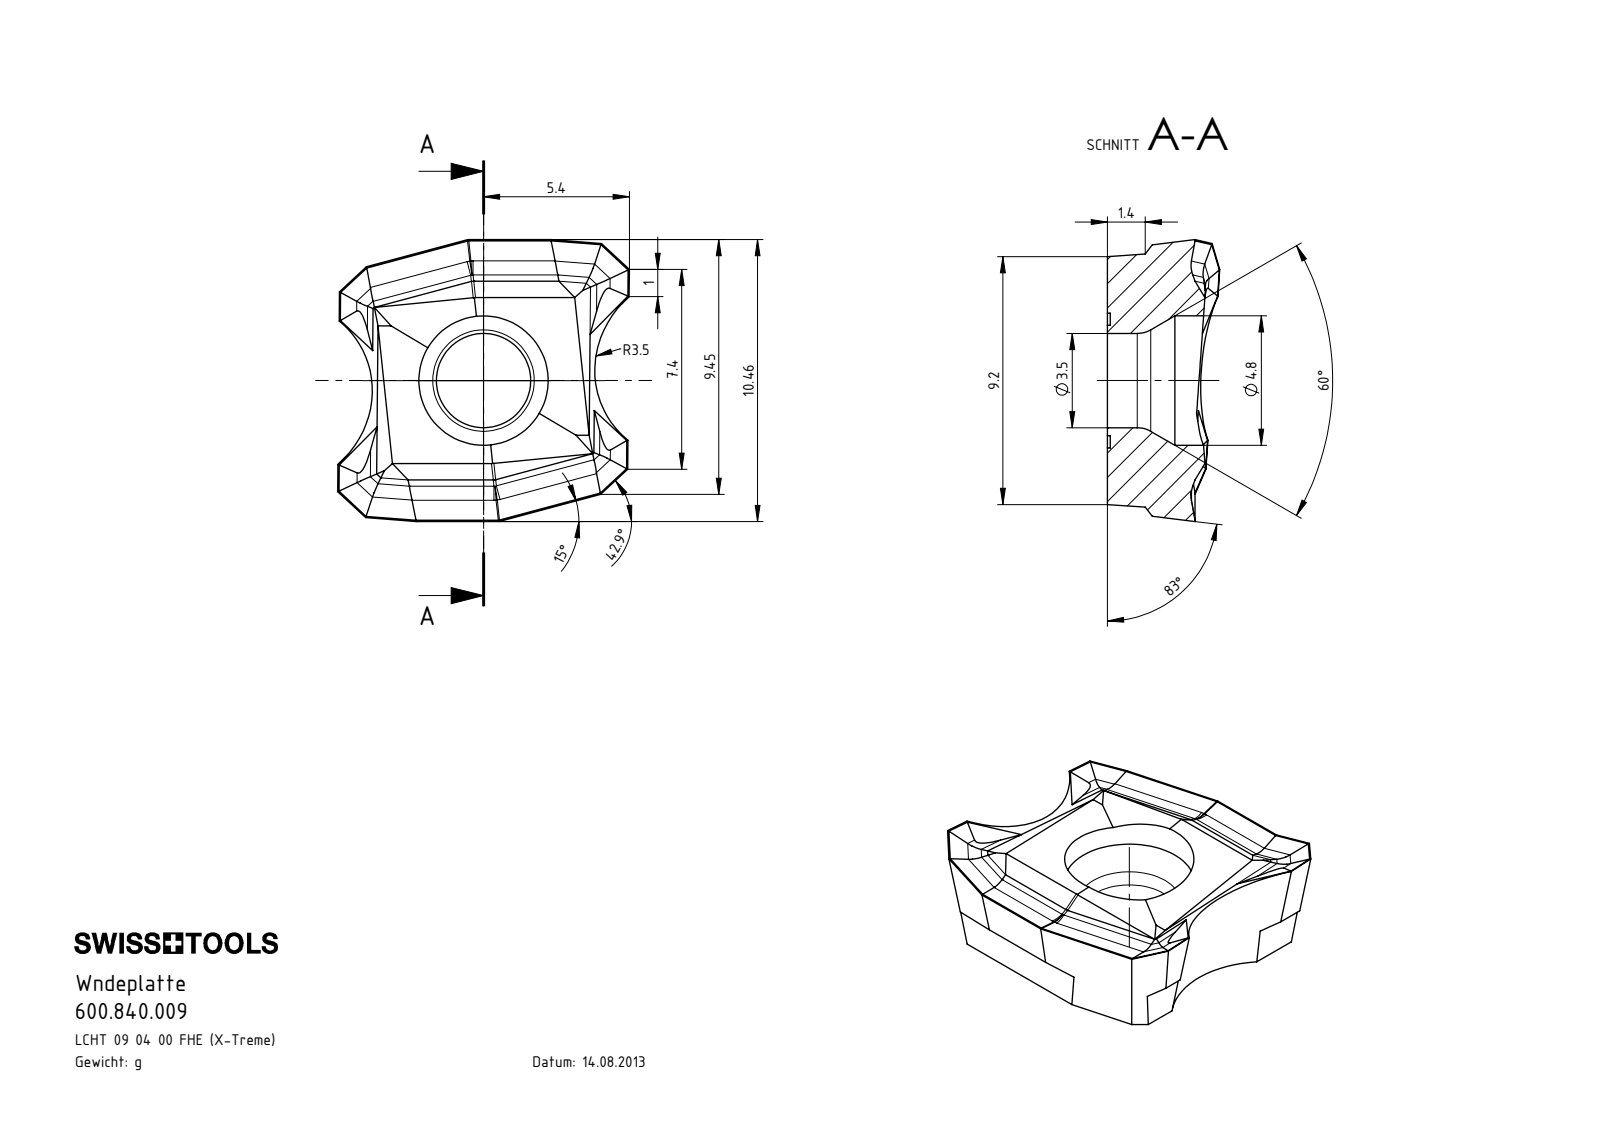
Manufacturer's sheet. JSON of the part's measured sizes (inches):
{"part_name": "600.840.009", "step_written_by": "SolidWorks 2022 (AUTOMOTIVE_DESIGN)", "units": "inches", "bodies": {"solids": 1, "faces": 132, "planar": 90, "cylindrical": 30, "other": 12}, "overall_size": [0.426, 0.412, 0.164], "volume_in3": 0.015, "surface_area_in2": 0.512, "round_holes": [[0.138, 1], [0.189, 1]], "round_bosses_or_shafts": [[0.161, 1]], "partial_cylinders_radius": [[0.039, 14], [0.028, 4], [0.026, 2]], "face_to_face_distances": [0.128, 0.124, 0.197, 0.236]}
